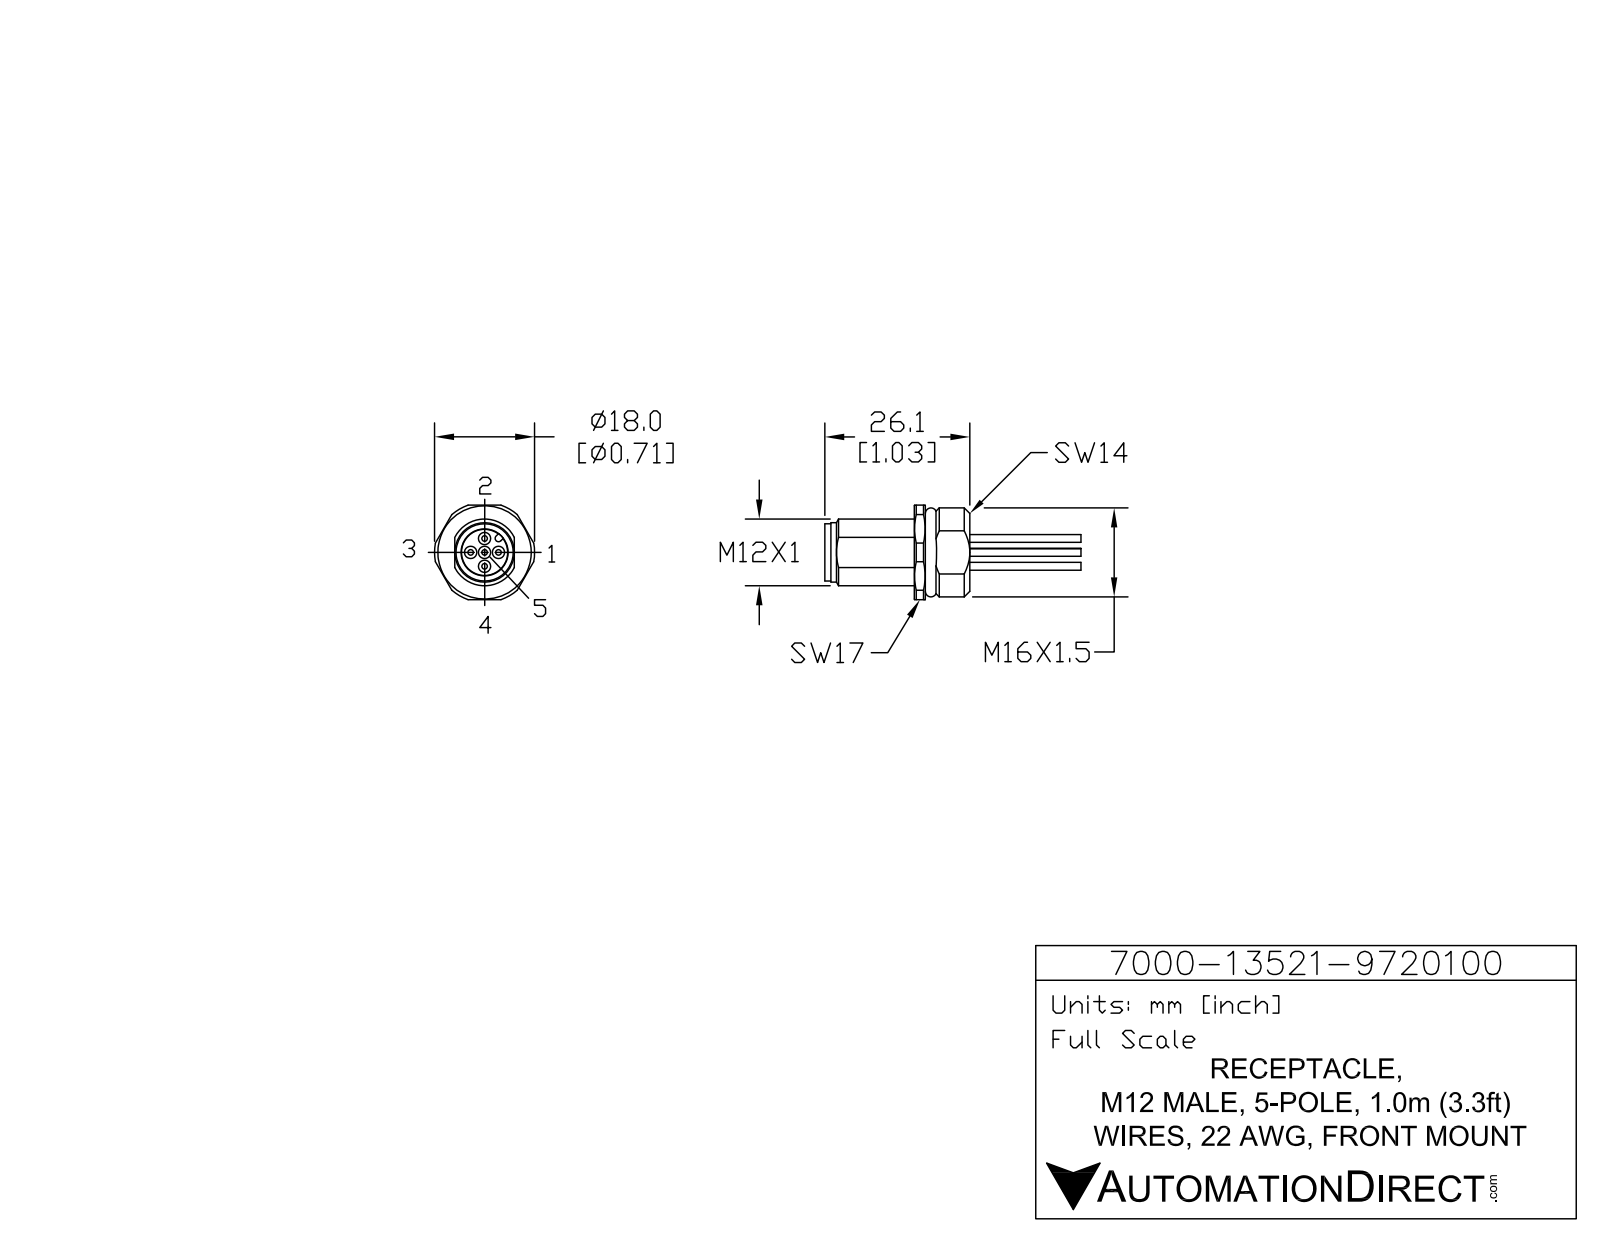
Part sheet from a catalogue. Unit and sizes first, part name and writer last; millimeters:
Units: millimetres
Overall size (bounding box): 46.1 × 18 × 17
Round holes (diameter × count): ⌀2.2 ×5, ⌀13 ×1
Round bosses / shafts (diameter × count): ⌀1.4 ×5, ⌀1 ×5, ⌀10.7 ×1, ⌀10.3 ×1
Partial cylindrical surfaces — rounded edges, fillets, slot ends (radius × count): R0.6 ×1, R6 ×1, R8 ×1, R9 ×1
Main face-to-face distances: 9, 1.65, 12.35, 10.7, 2, 7, 14, 17, 16.2, 9.2
Hole centre spacings: 2.5, 3.54, 5
Volume: 3 245 mm³ · Surface area: 2 495 mm²
Bodies: 1 solid, 109 faces (35 planar, 48 cylindrical, 26 other)
Part name (STEP PRODUCT): 7231-13521-9720100
STEP written by: SolidWorks 2015 (AUTOMOTIVE_DESIGN)
